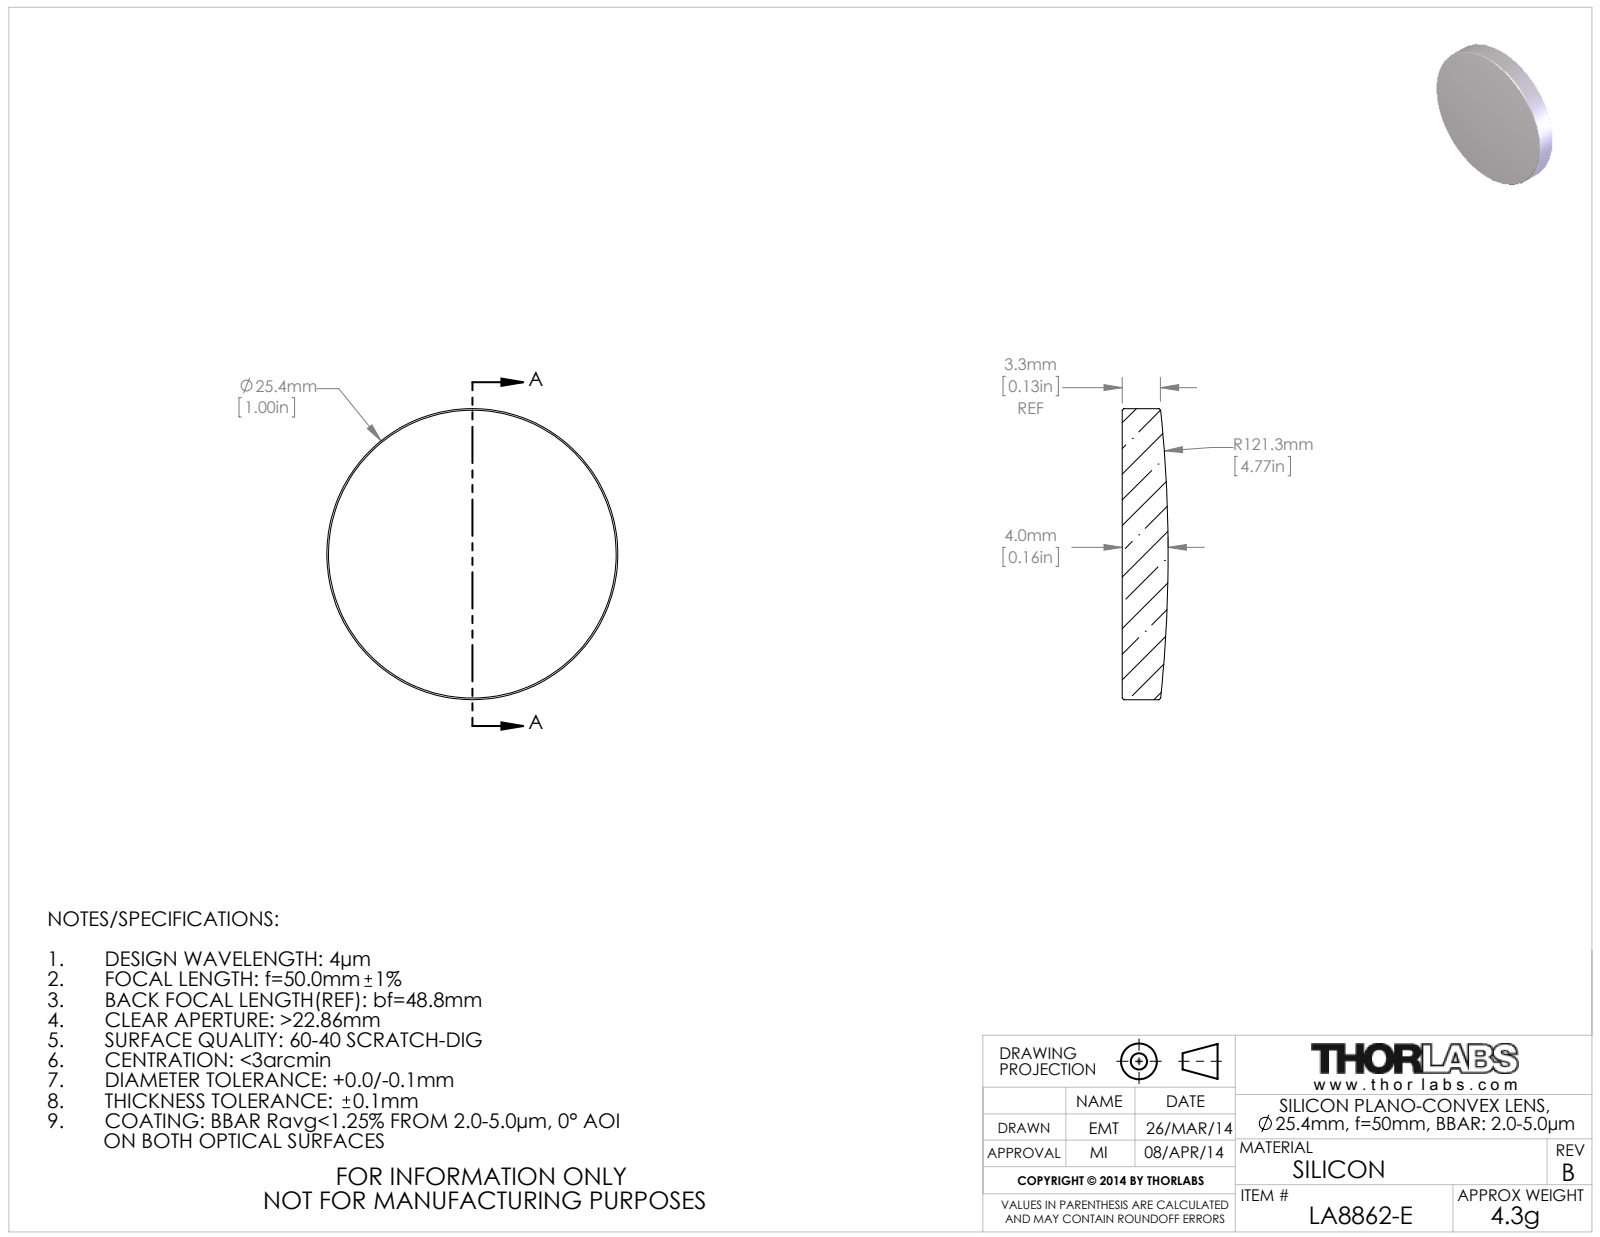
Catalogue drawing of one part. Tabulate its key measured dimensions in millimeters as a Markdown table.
| quantity | value |
| --- | --- |
| part name | 20117-E0W |
| STEP written by | SolidWorks 2014 (CONFIG_CONTROL_DESIGN) |
| units | millimeters |
| bodies | 1 solid, 9 faces (1 planar, 2 cylindrical, 6 other) |
| overall size | 25.4 × 25.4 × 4 |
| volume | 1 857 mm³ |
| surface area | 1 269 mm² |
| round bosses / shafts (diameter × count) | 25.4 × 1 |
